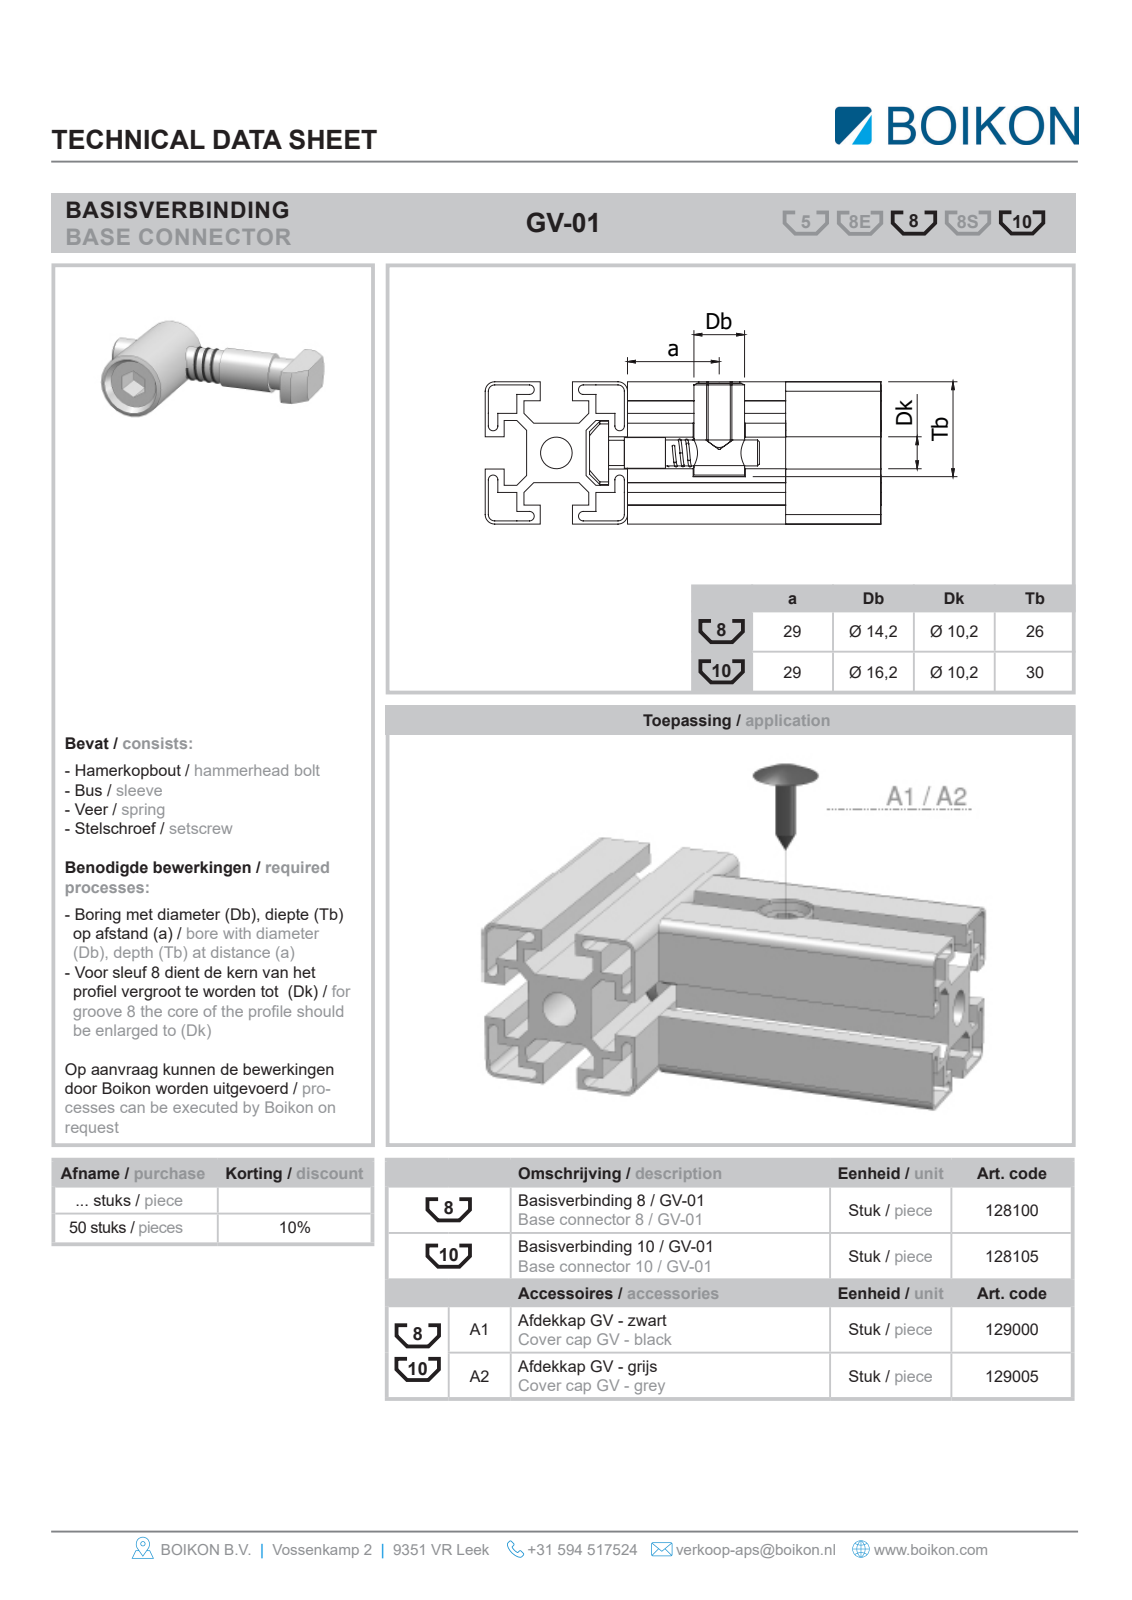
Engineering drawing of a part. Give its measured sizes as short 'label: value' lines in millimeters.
name: Root; 128100Basisverbinding 8 / GV-01BOIKON
written by: HiCAD 2013 1802.4 Build 509 (AUTOMOTIVE_DESIGN)
unit: mm
bodies: 1 solid, 27 faces (17 planar, 7 cylindrical, 3 other)
size: 51.7 × 26.65 × 14
volume: 6 111 mm³; area: 2 783 mm²
bosses: 1× ⌀14, 1× ⌀9.8, 1× ⌀8.3
rounds: 1× R8.5
face distances: 24, 5, 8.3, 6, 36.2, 42.2, 31.2, 37.2, 9.5, 14.5
